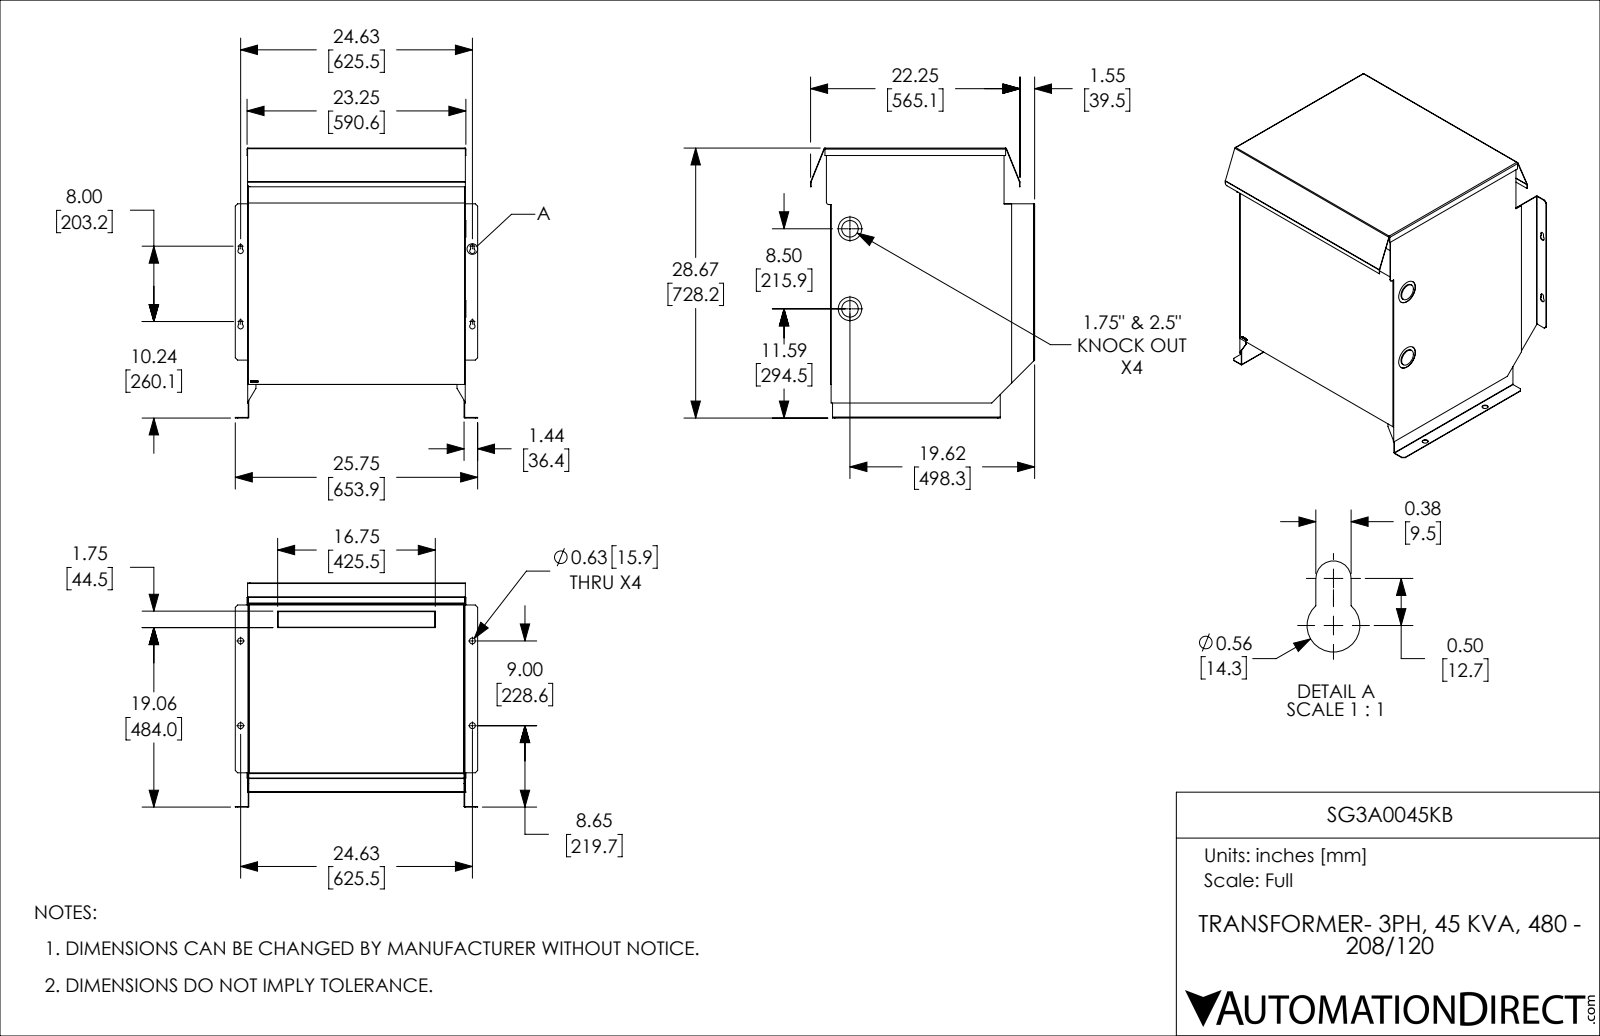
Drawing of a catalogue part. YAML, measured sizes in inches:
part_name: "SG3A0045KB"
step_written_by: "SolidWorks 2018 (AUTOMOTIVE_DESIGN)"
units: inches
bodies: {solids: 7, faces: 332, planar: 217, cylindrical: 81, other: 34}
overall_size: [28.668, 25.745, 23.801]
volume: 205.5
surface_area: 7302
round_holes:
  - {diameter: 0.625, count: 4}
  - {diameter: 2.5, count: 2}
round_bosses_or_shafts:
  - {diameter: 1.75, count: 2}
partial_cylinders:
  - {radius: 0.03, count: 12}
  - {radius: 0.09, count: 12}
  - {radius: 0.06, count: 6}
  - {radius: 0.11, count: 6}
  - {radius: 0.188, count: 4}
  - {radius: 0.281, count: 4}
  - {radius: 0.25, count: 3}
face_to_face_distances: [0.06, 0.05, 23.055, 22.995, 23.115, 17.996, 18.046, 18.056, 18.106, 25.058]
hole_center_spacings: [9, 24.625, 26.218, 8.5]
